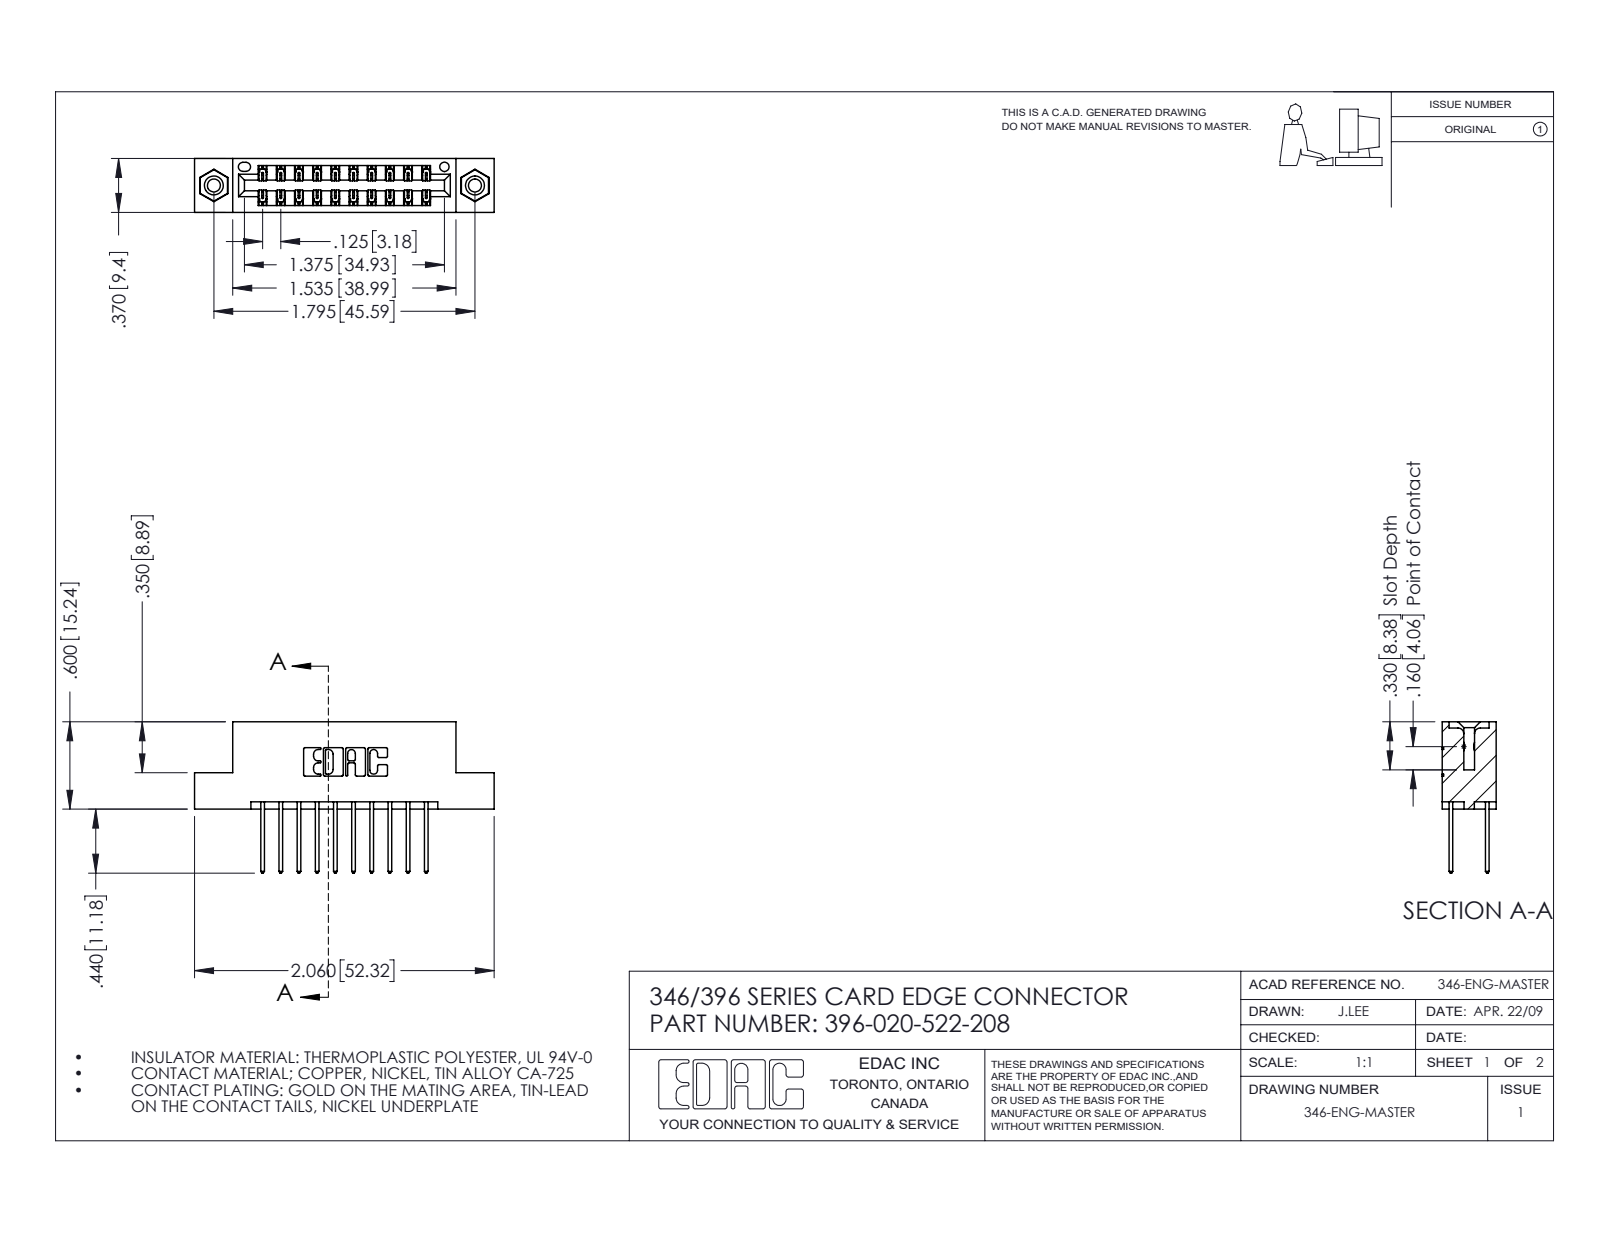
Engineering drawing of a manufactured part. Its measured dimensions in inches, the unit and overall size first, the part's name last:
Units: inches
Overall size (bounding box): 2.06 × 1.04 × 0.37
Round holes (diameter × count): ⌀0.089 ×2, ⌀0.125 ×2, ⌀0.156 ×2, ⌀0.064 ×1
Round bosses / shafts (diameter × count): ⌀0.155 ×2
Partial cylindrical surfaces — rounded edges, fillets, slot ends (radius × count): R0.006 ×30, R0.01 ×22, R0.01 ×20, R0.007 ×6, R0.031 ×6, R0.026 ×3, R0.014 ×2, R0.022 ×2
Main face-to-face distances: 0.25, 0.048, 0.322, 0.37, 0.072, 0.298, 0.025, 0.275, 0.148, 0.222
Hole centre spacings: 0.246, 1.59, 1.795
Volume: 0.299 in³ · Surface area: 10.06 in²
Bodies: 23 solids, 1222 faces (808 planar, 398 cylindrical, 16 other)
Part name (STEP PRODUCT): 346 Part_Flush Mounting Lugs - 0.156 Dia-TI; 396-020-522-208; 345-292-001_345-293-122; 345-250-001_345-250-003-102
STEP written by: SolidWorks 2016 (CONFIG_CONTROL_DESIGN)
